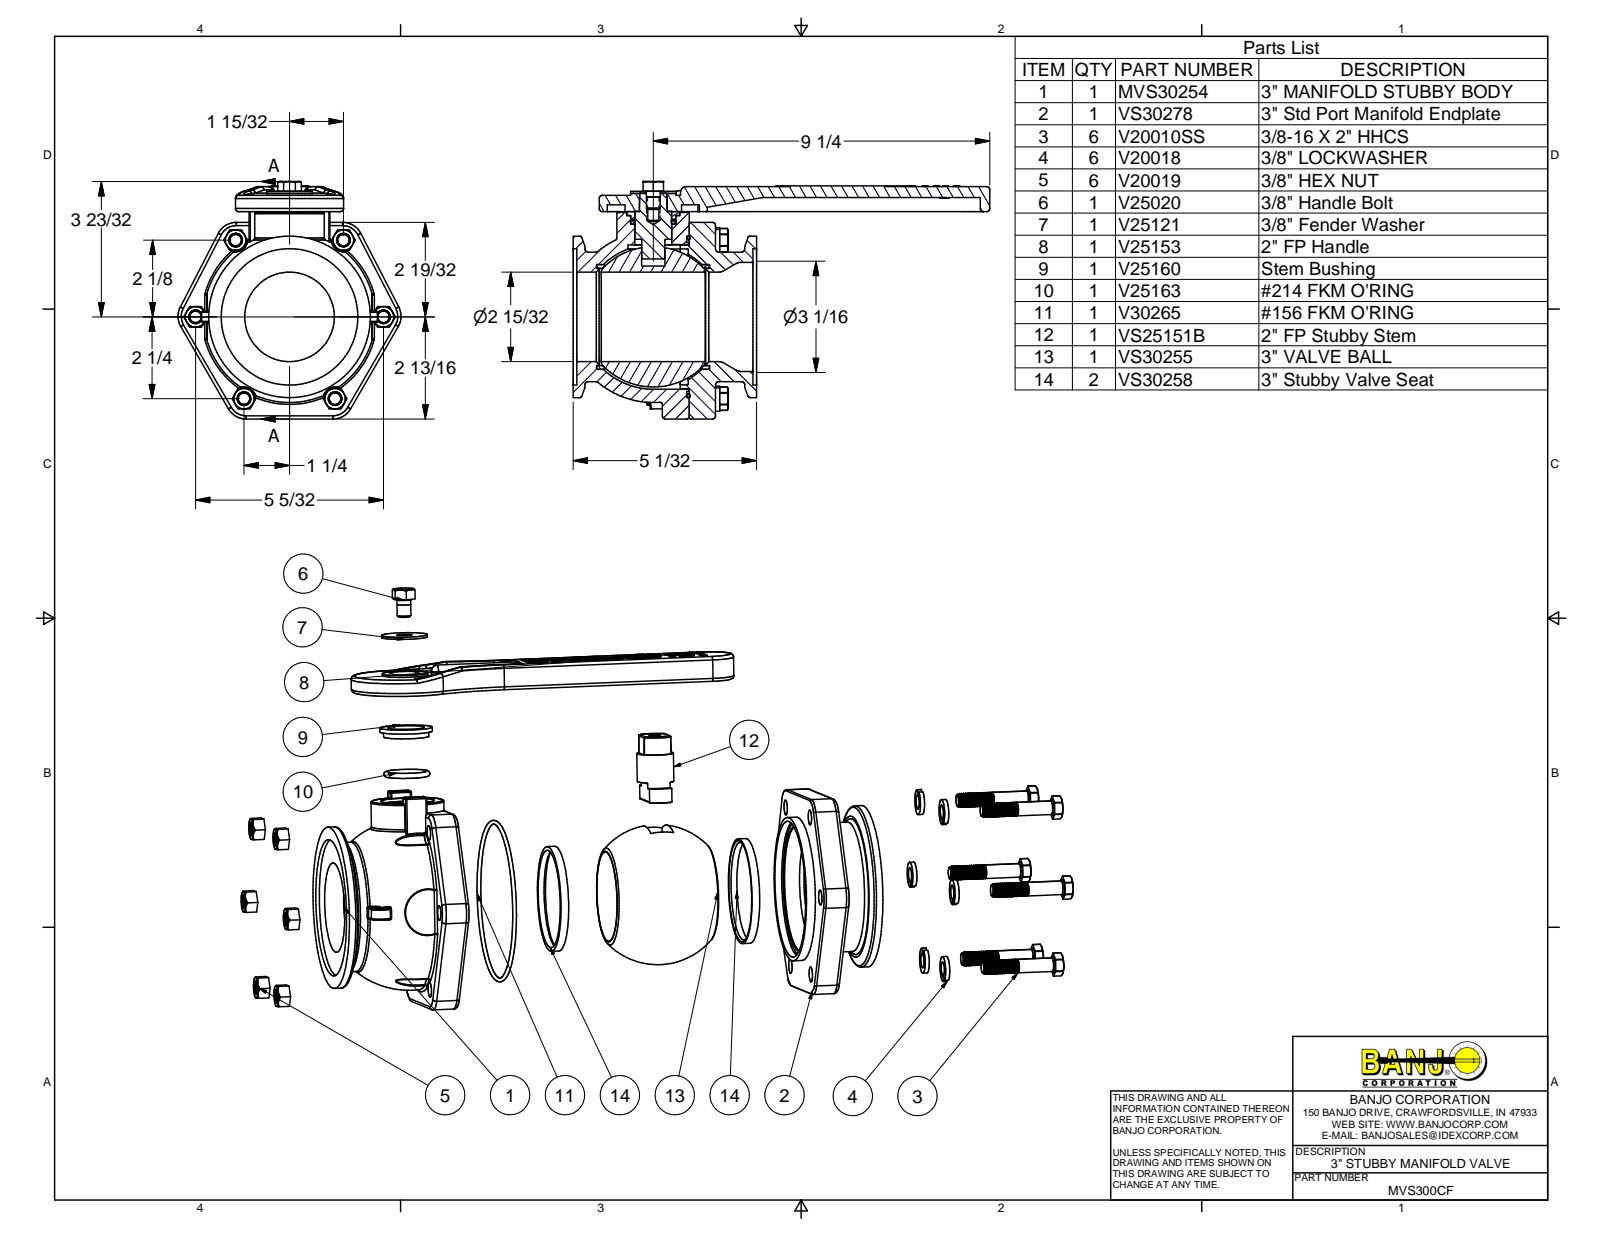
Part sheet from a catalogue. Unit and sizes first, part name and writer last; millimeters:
Units: millimetres
Overall size (bounding box): 290.58 × 165.91 × 155.55
Round holes (diameter × count): ⌀10.31 ×7, ⌀7.81 ×6, ⌀9.78 ×6, ⌀7.87 ×2, ⌀7.8 ×1, ⌀17.29 ×1, ⌀24.43 ×1, ⌀25.4 ×1, ⌀25.81 ×1, ⌀31.5 ×1, ⌀37.08 ×1, ⌀62.48 ×1
Round bosses / shafts (diameter × count): ⌀8.24 ×90, ⌀9.52 ×7, ⌀17.46 ×6, ⌀112.78 ×1, ⌀104.09 ×1, ⌀100.2 ×1, ⌀90.42 ×1, ⌀75.41 ×1
Partial cylindrical surfaces — rounded edges, fillets, slot ends (radius × count): R2.29 ×32, R0.76 ×16, R4.12 ×12, R0.81 ×6, R8.12 ×6, R14.22 ×6, R7.94 ×4, R1.5 ×2
Main face-to-face distances: 18.28, 2.54, 125.35, 6.61, 96.77, 78.49, 37.08, 18.8, 59.69, 7.62
Hole centre spacings: 60.44, 63.82, 65.38, 65.46, 65.53, 66.39, 110.89, 112.83
Volume: 1 101 000 mm³ · Surface area: 274 972 mm²
Bodies: 30 solids, 2292 faces (625 planar, 764 cylindrical, 903 other)
Part name (STEP PRODUCT): MVS30254X; MVS30254; VS30278X; VS30278 (+8 more)
STEP written by: Autodesk Inventor 2014 (AUTOMOTIVE_DESIGN)
